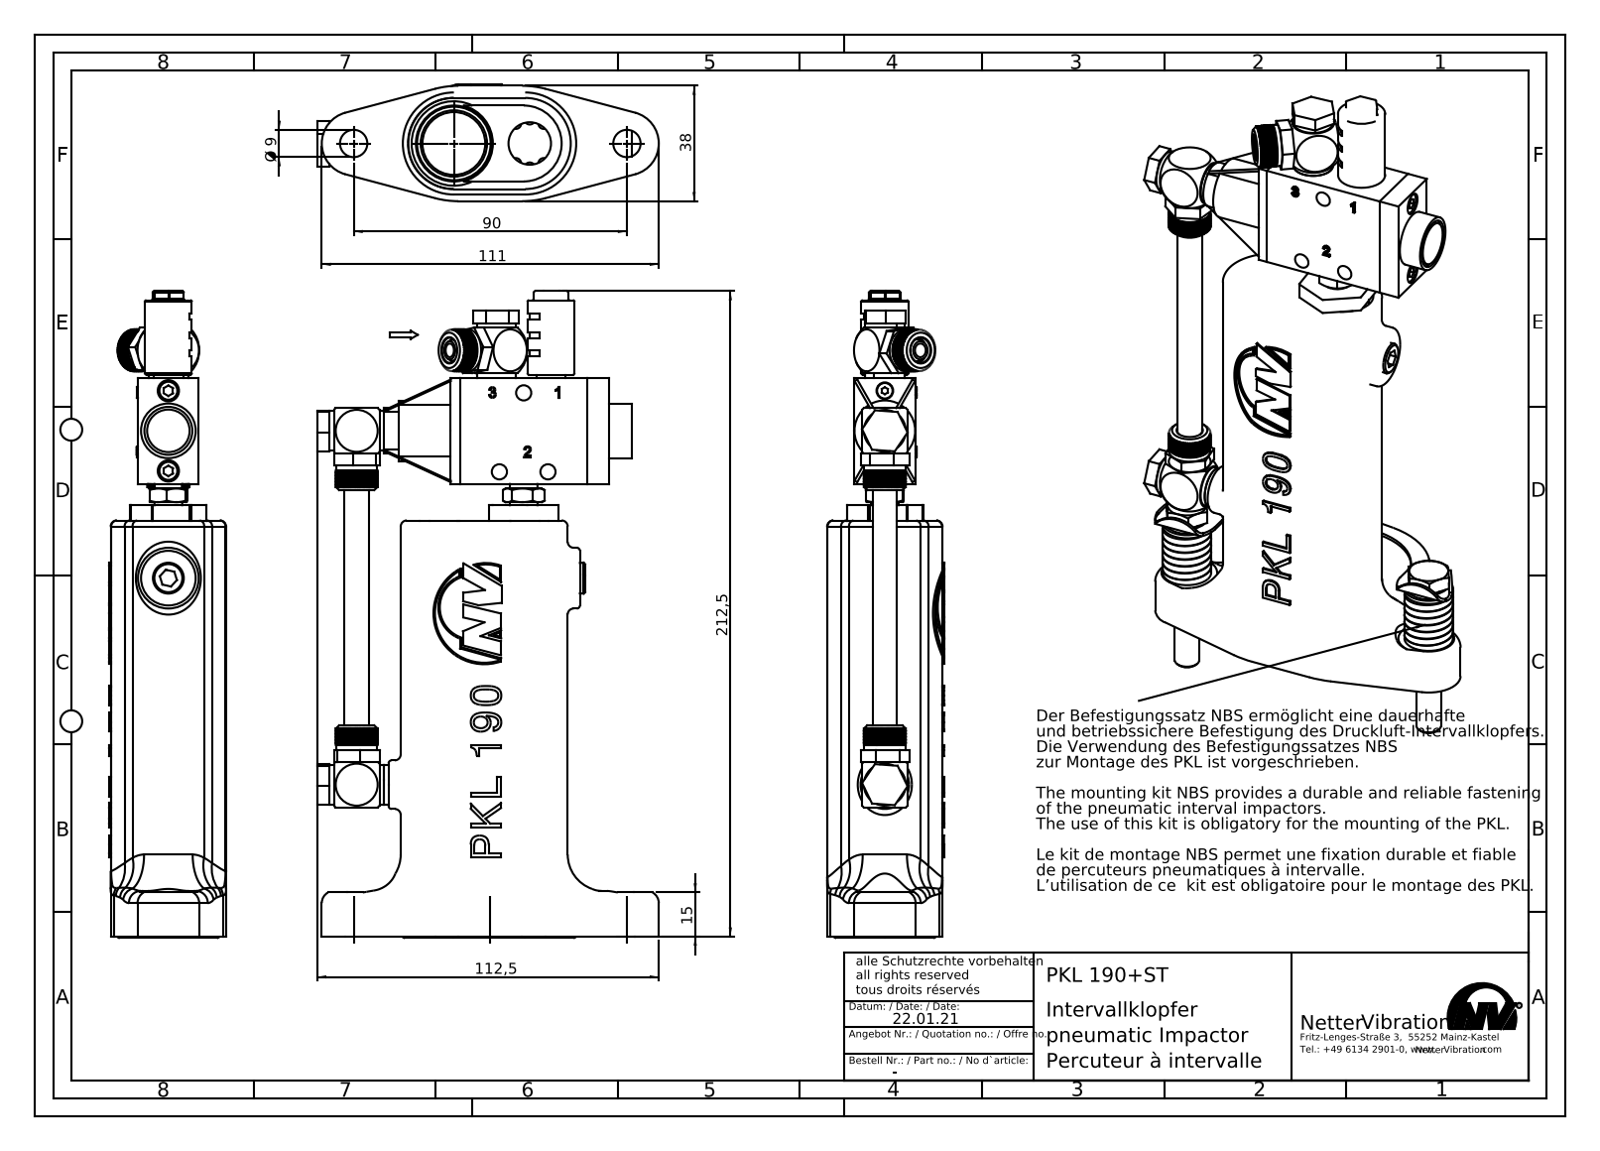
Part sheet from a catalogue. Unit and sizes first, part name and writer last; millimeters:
Units: millimetres
Overall size (bounding box): 231.4 × 111.5 × 47.5
Round holes (diameter × count): ⌀3.5 ×6, ⌀8.57 ×6, ⌀4.5 ×5, ⌀5 ×4, ⌀10 ×3, ⌀10.1 ×3, ⌀2.5 ×2, ⌀3 ×2, ⌀3.4 ×2, ⌀7 ×2, ⌀8.3 ×2, ⌀8.4 ×2
Round bosses / shafts (diameter × count): ⌀13 ×5, ⌀9.73 ×4, ⌀16 ×3, ⌀9.67 ×3, ⌀8.5 ×3, ⌀8 ×3, ⌀20 ×2, ⌀13.65 ×2
Partial cylindrical surfaces — rounded edges, fillets, slot ends (radius × count): R0.5 ×24, R4 ×8, R10.5 ×6, R2 ×5, R19.65 ×4, R30 ×4, R40 ×4, R1 ×3
Main face-to-face distances: 9, 29, 38, 20, 1, 137, 42, 9.5, 5, 35
Hole centre spacings: 115.2, 9, 13.2, 27.2, 2, 16, 18, 24
Volume: 333 974 mm³ · Surface area: 87 441 mm²
Bodies: 33 solids, 5300 faces (1069 planar, 1482 cylindrical, 2749 other)
Part name (STEP PRODUCT): PKL 190 ST
STEP written by: SolidWorks 2015 (AUTOMOTIVE_DESIGN)
